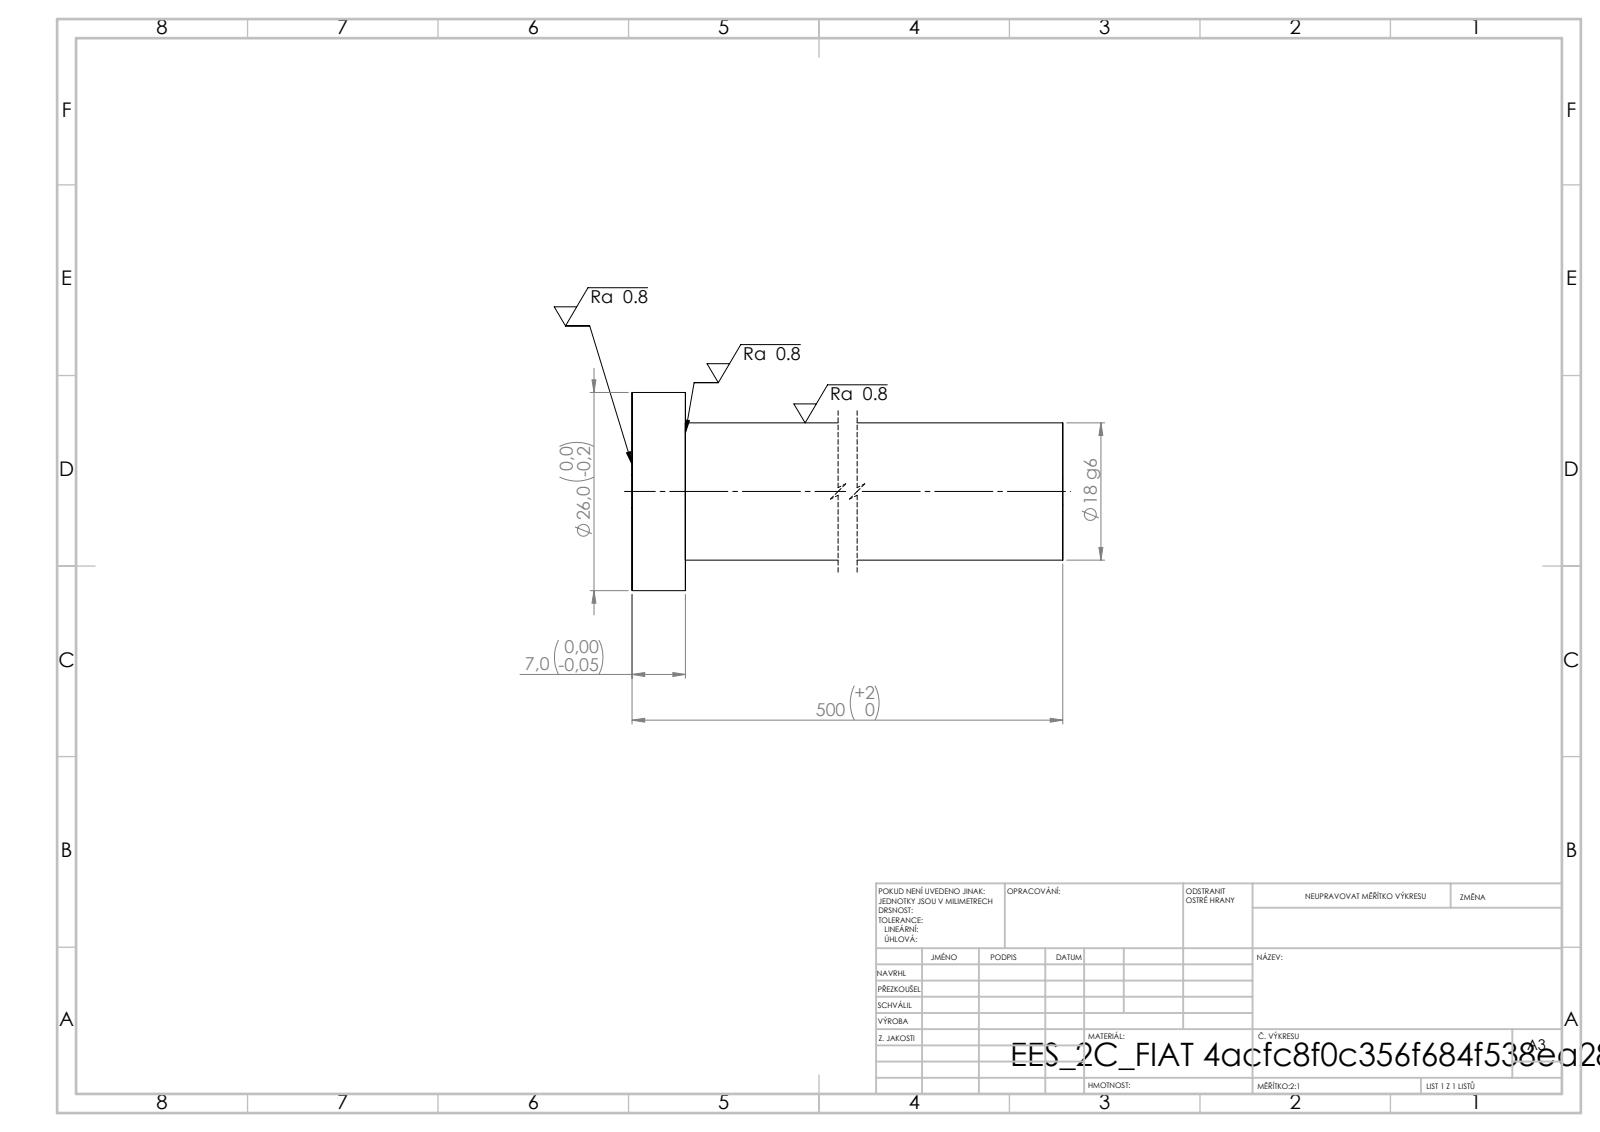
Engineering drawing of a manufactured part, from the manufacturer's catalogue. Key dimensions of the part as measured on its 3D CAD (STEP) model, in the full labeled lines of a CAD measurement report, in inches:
STEP written by: SolidWorks 2019 (CONFIG_CONTROL_DESIGN)
Units: inches
Bodies: 1 solid, 7 faces (3 planar, 4 cylindrical, 0 other)
Overall size (bounding box): 19.685 × 1.024 × 1.024
Volume: 7.882 in³ · Surface area: 45.74 in²
Round bosses / shafts (diameter × count): ⌀1.024 ×1, ⌀0.709 ×1
Main face-to-face distances: 0.276, 19.685, 19.409
